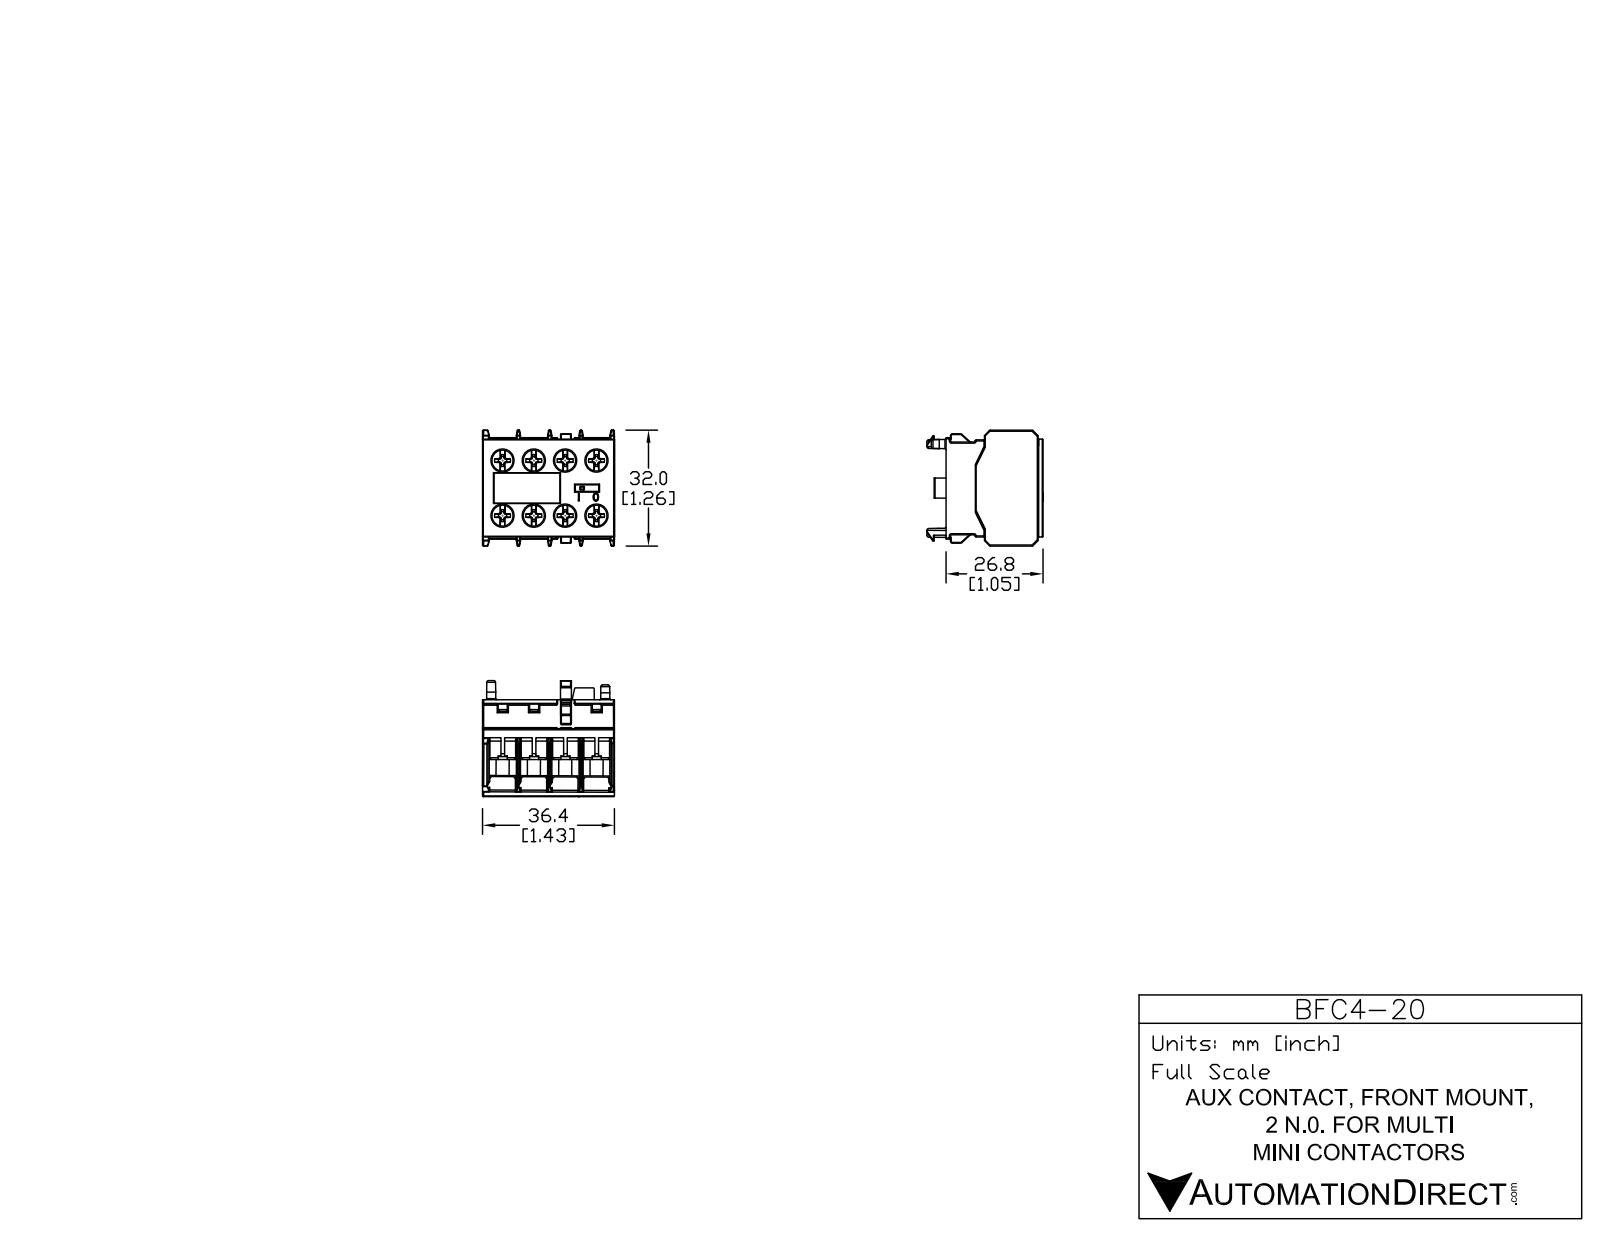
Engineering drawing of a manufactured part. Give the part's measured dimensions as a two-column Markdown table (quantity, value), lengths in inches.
| quantity | value |
| --- | --- |
| part name | BFC4-20 |
| STEP written by | SolidWorks 2013 (AUTOMOTIVE_DESIGN) |
| units | inches |
| bodies | 20 solids, 761 faces (593 planar, 168 cylindrical, 0 other) |
| overall size | 1.437 × 1.269 × 1.26 |
| volume | 1.002 in³ |
| surface area | 26.95 in² |
| round holes (diameter × count) | 0.236 × 8 |
| round bosses / shafts (diameter × count) | 0.197 × 8, 0.118 × 8, 0.108 × 3 |
| partial cylindrical surfaces (radius × count) | 0.02 × 8, 0.178 × 8, 0.012 × 6, 0.01 × 4, 0.006 × 2, 0.007 × 2, 0.008 × 2 |
| main face-to-face distances | 0.049, 0.679, 0.34, 0.63, 0.339, 1.019, 0.291, 0.728, 0.389, 0.29 |
| hole center spacings | 0.34, 0.591, 0.679, 0.681, 0.9, 0.339, 0.681, 1.019 |
